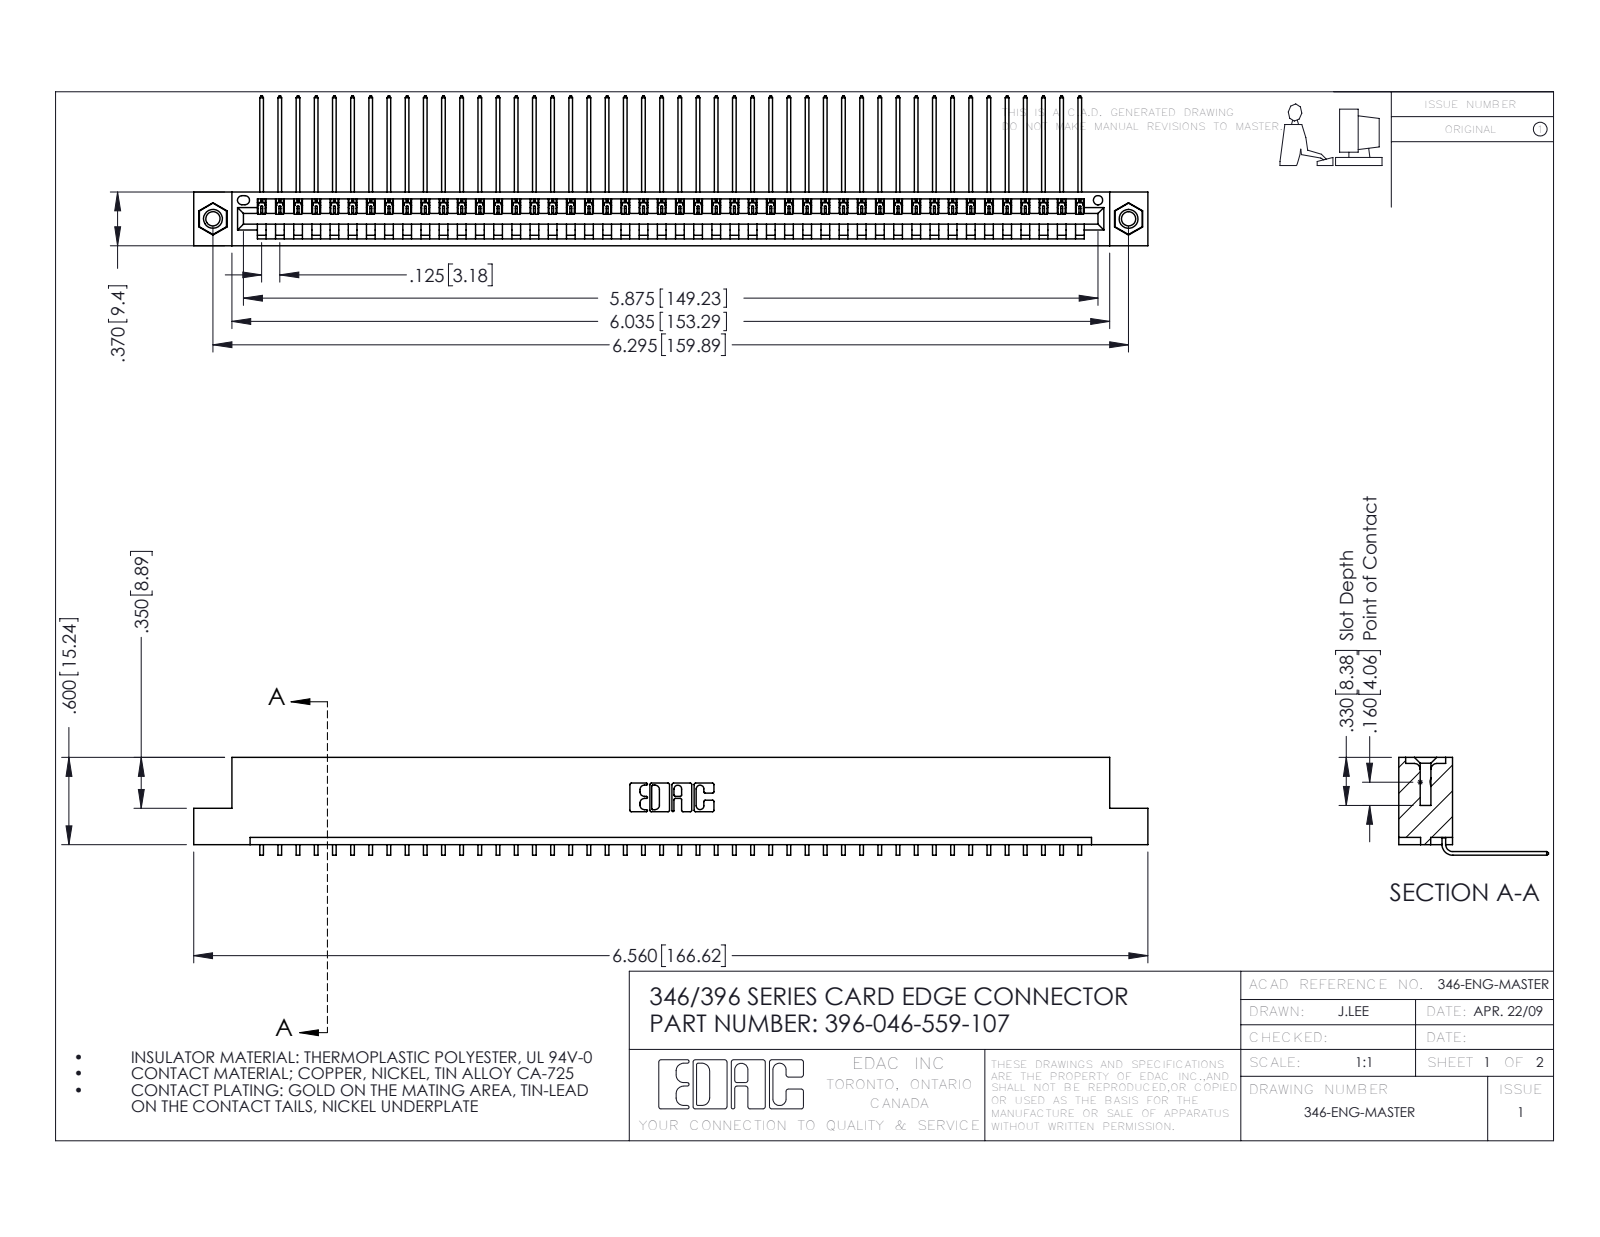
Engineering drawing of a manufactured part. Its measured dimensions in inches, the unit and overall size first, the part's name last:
Units: inches
Overall size (bounding box): 6.56 × 1.03 × 0.673
Round holes (diameter × count): ⌀0.098 ×2, ⌀0.125 ×2, ⌀0.156 ×2, ⌀0.064 ×1
Round bosses / shafts (diameter × count): ⌀0.155 ×2
Partial cylindrical surfaces — rounded edges, fillets, slot ends (radius × count): R0.006 ×92, R0.01 ×22, R0.007 ×6, R0.031 ×6, R0.026 ×3, R0.031 ×2, R0.04 ×2, R0.014 ×1
Main face-to-face distances: 0.048, 0.322, 0.37, 0.025, 0.25, 0.072, 0.298, 0.148, 0.222, 0.1
Hole centre spacings: 0.246, 6.086, 6.295
Volume: 0.984 in³ · Surface area: 32.76 in²
Bodies: 49 solids, 2942 faces (2040 planar, 886 cylindrical, 16 other)
Part name (STEP PRODUCT): 346 Part_Flush Mounting Lugs - 0.156 Dia-TI; 396-046-559-107; 345-250-001_345-250-005-103; 345-292-001_558 559 Tail - 1
STEP written by: SolidWorks 2016 (CONFIG_CONTROL_DESIGN)
